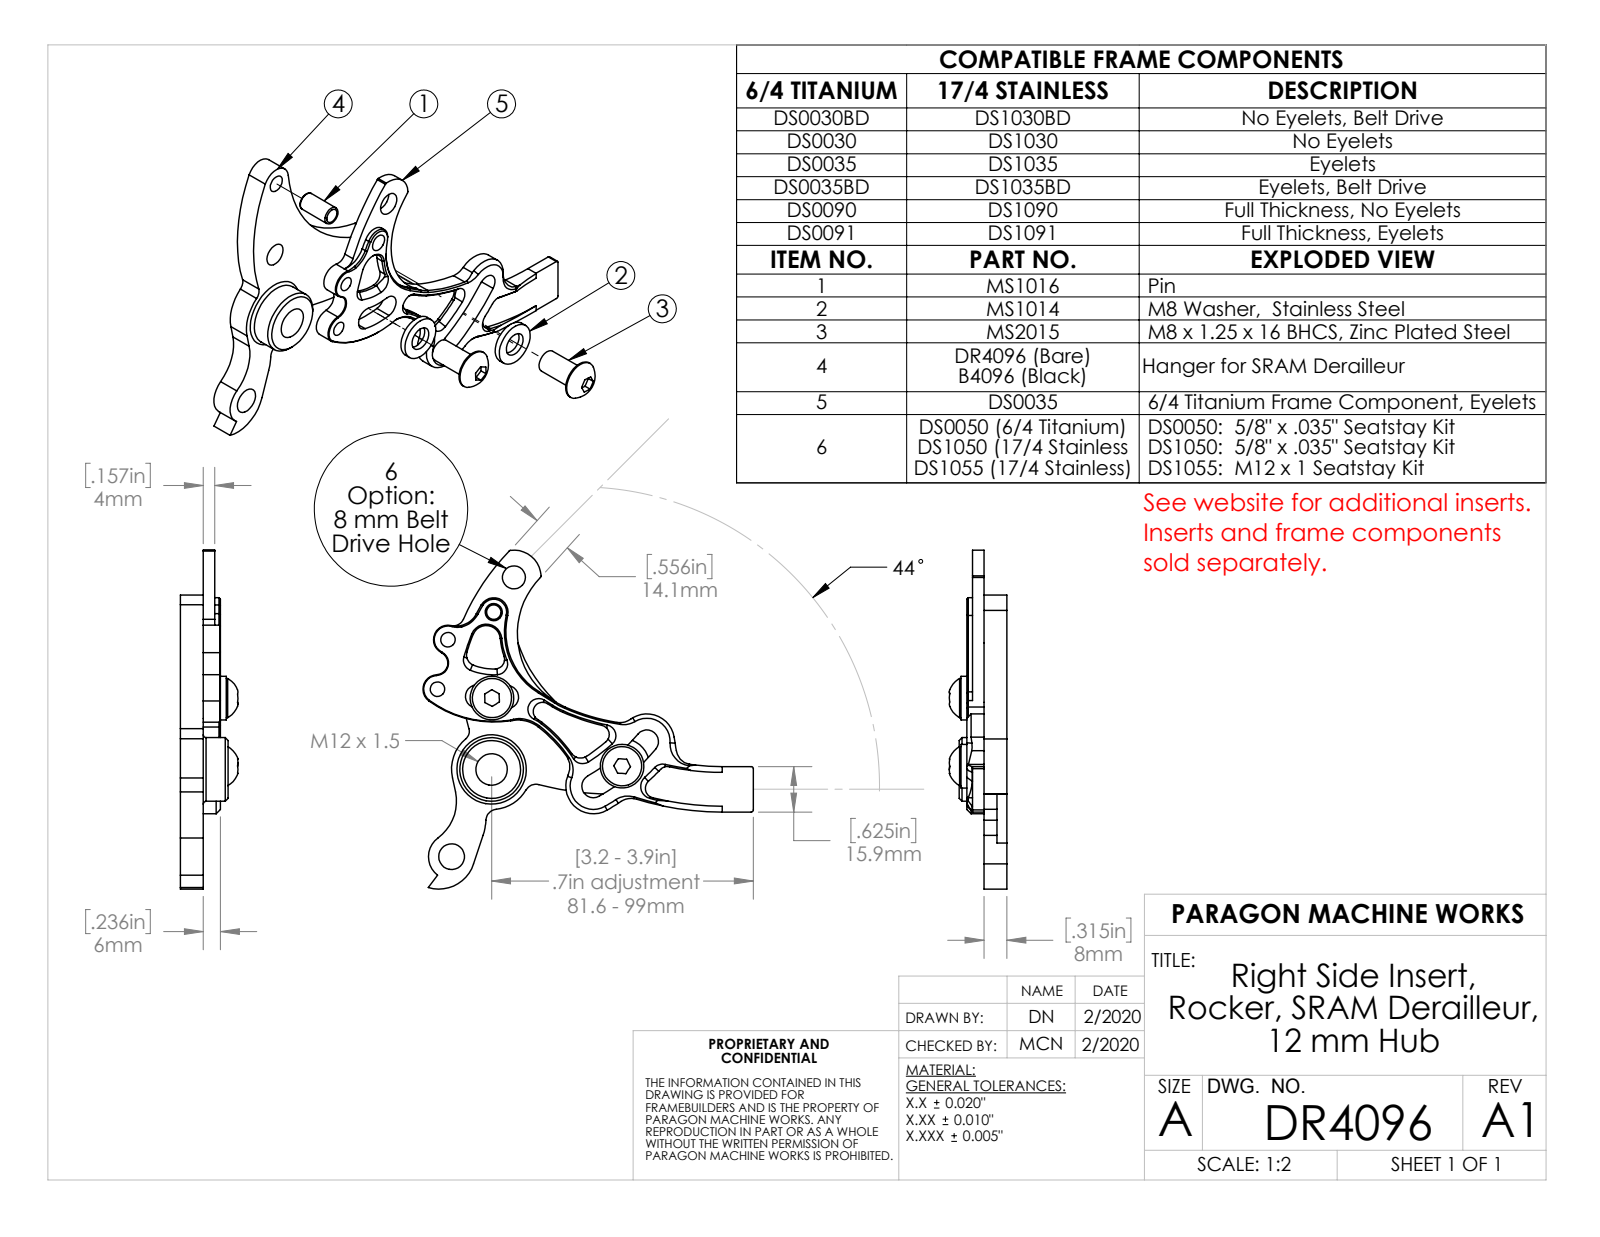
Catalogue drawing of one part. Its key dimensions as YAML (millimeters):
part_name: "DR4096"
step_written_by: "SolidWorks 2019 (AUTOMOTIVE_DESIGN)"
units: millimeters
bodies: {solids: 1, faces: 63, planar: 14, cylindrical: 45, other: 4}
overall_size: [104.73, 71.03, 16.65]
volume: 18890
surface_area: 10406
round_holes:
  - {diameter: 5.99, count: 1}
  - {diameter: 8, count: 1}
  - {diameter: 8, count: 1}
  - {diameter: 9, count: 1}
  - {diameter: 11, count: 1}
  - {diameter: 12.13, count: 1}
round_bosses_or_shafts:
  - {diameter: 22.22, count: 1}
partial_cylinders:
  - {radius: 3.81, count: 2}
  - {radius: 4, count: 2}
  - {radius: 20, count: 2}
  - {radius: 3.3, count: 1}
  - {radius: 5.99, count: 1}
  - {radius: 6.68, count: 1}
  - {radius: 7.35, count: 1}
  - {radius: 7.65, count: 1}
face_to_face_distances: [8, 3.5, 4.5, 1, 8.65, 12.15, 13.15, 16.65, 19.99]
hole_center_spacings: [24.92, 30, 33.5, 45.59, 51.29, 54.92, 57.13, 67.41]
